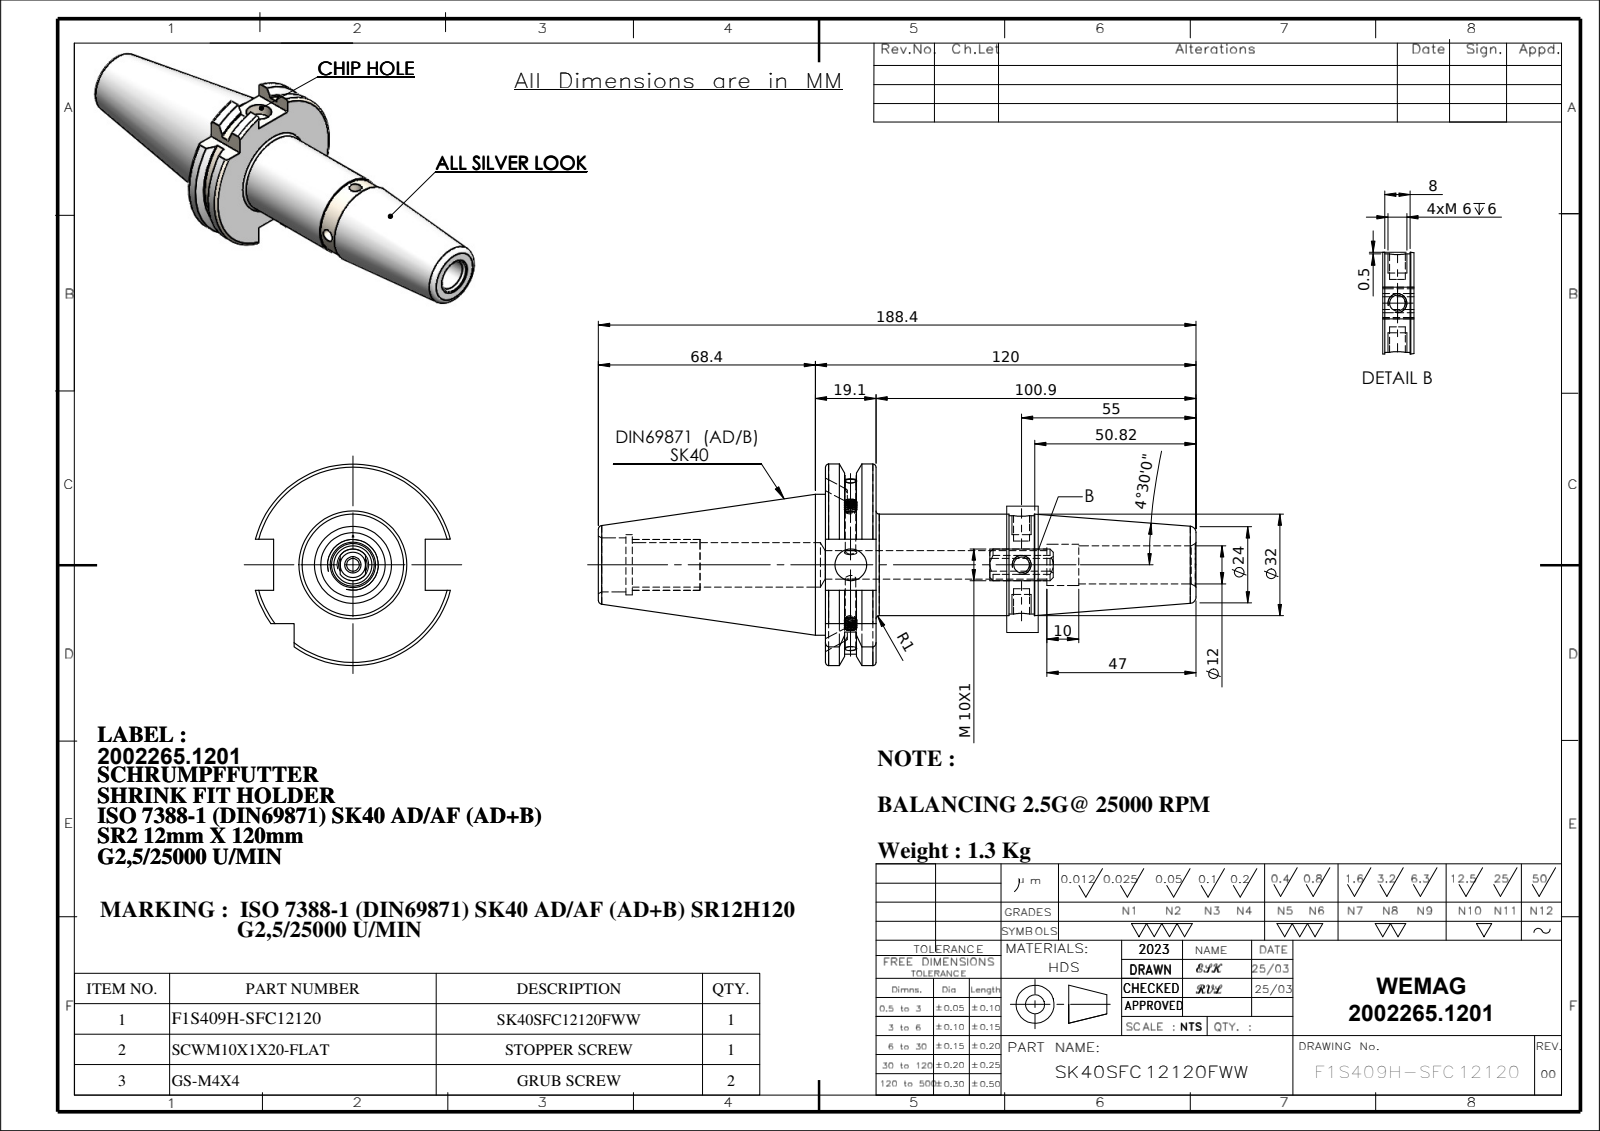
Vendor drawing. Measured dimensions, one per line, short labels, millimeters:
name: 91406-SR212120; SK40SFC12120FWW; GS-M4X4_DIN 913 - M4 x 4-N; SCWM10X1X20-FLAT
written by: SolidWorks 2018 (CONFIG_CONTROL_DESIGN)
unit: mm
bodies: 4 solids, 231 faces (58 planar, 71 cylindrical, 102 other)
size: 188.4 × 63.55 × 61.48
volume: 162 754 mm³; area: 35 311 mm²
holes: 2× ⌀5, 1× ⌀3.3, 1× ⌀4, 1× ⌀9, 1× ⌀10, 1× ⌀11.99, 1× ⌀12.99, 1× ⌀14, 1× ⌀17, 1× ⌀19
bosses: 2× ⌀4, 1× ⌀44.45, 1× ⌀32, 1× ⌀31
rounds: 1× R5, 1× R28.12, 1× R31.77
face distances: 15.9, 8, 16.1, 47.8, 116.8, 100.9, 71.6, 87.5, 188.4, 10.7
hole spacings: 53.85
